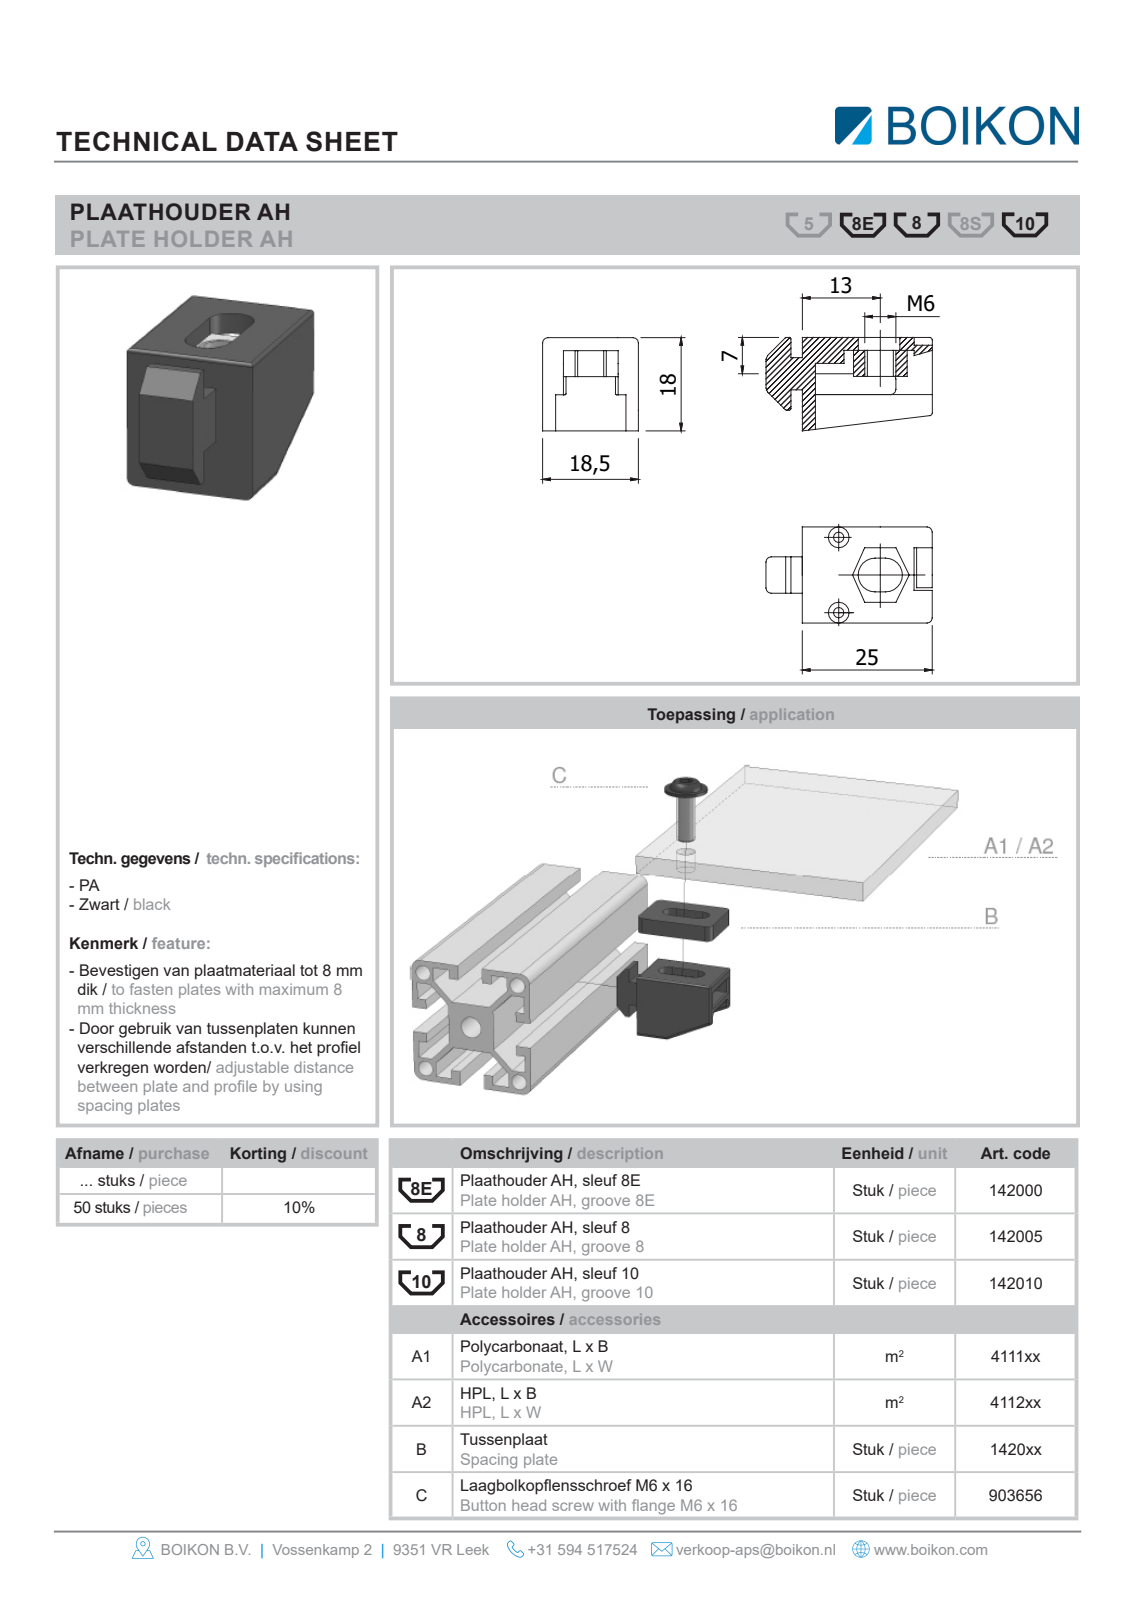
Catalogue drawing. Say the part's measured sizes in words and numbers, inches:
The part is named "Root; 142005Plaathouder AH, sleuf 8BOIKON". Its 3-D file was written by "HiCAD 2013 1802.4 Build 509 (AUTOMOTIVE_DESIGN)". It is 1 solid with 32 faces: 29 planar, 3 cylindrical and 0 other. Overall it measures 1.339 by 0.789 by 0.728 inches. Its volume is 0.364 cubic inches and its surface area 5.65 square inches. Round holes: 1 of diameter 0.236. Partial cylindrical surfaces (rounded edges, fillets, slot ends): 2 of radius 0.128. The main face-to-face distances are 0.098, 0.728, 0.394, 0.63, 0.984, 0.211, 0.518, 0.112, 0.419, 0.531.
